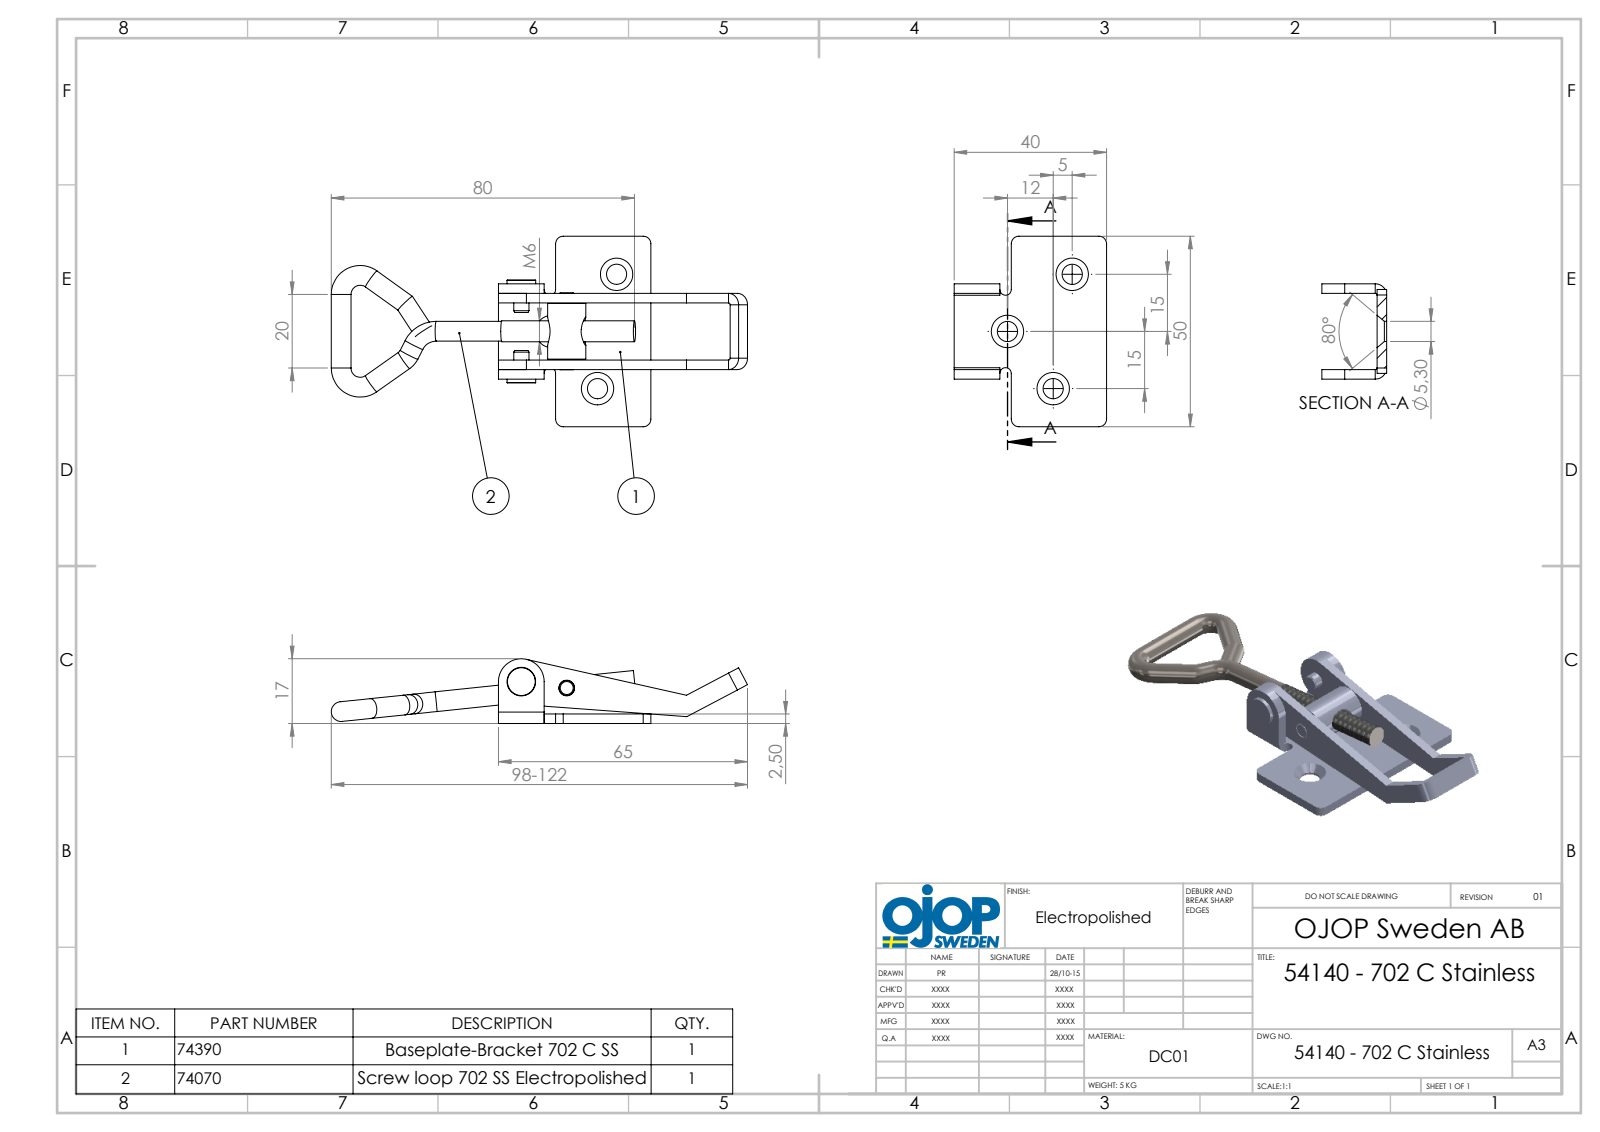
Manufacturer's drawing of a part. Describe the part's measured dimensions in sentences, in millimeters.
The part is named "702 - C; 54140 - 702 C RF; 702 - Skruvögla; 702 - Rulle (+2 more)". Its 3-D file was written by "SolidWorks 2015 (AUTOMOTIVE_DESIGN)". It is 6 solids with 160 faces: 57 planar, 71 cylindrical and 32 other. Overall it measures 113.58 by 50 by 17 millimeters. Its volume is 11 364 cubic millimeters and its surface area 10 872 square millimeters. Round holes: 3 of diameter 5.3, 2 of diameter 4.1, 1 of diameter 5, 1 of diameter 6. Round bosses or shafts: 6 of diameter 5.18, 2 of diameter 4, 1 of diameter 10, 1 of diameter 7.5, 1 of diameter 5.5. Partial cylindrical surfaces (rounded edges, fillets, slot ends): 4 of radius 0.5, 4 of radius 2, 4 of radius 3, 2 of radius 1.5, 1 of radius 6. The main face-to-face distances are 2.5, 17.5, 20, 15, 5, 22.5, 25, 19.8, 5.2, 2.7. The hole center spacings are 12.02, 19.21, 22.67, 30.41.
